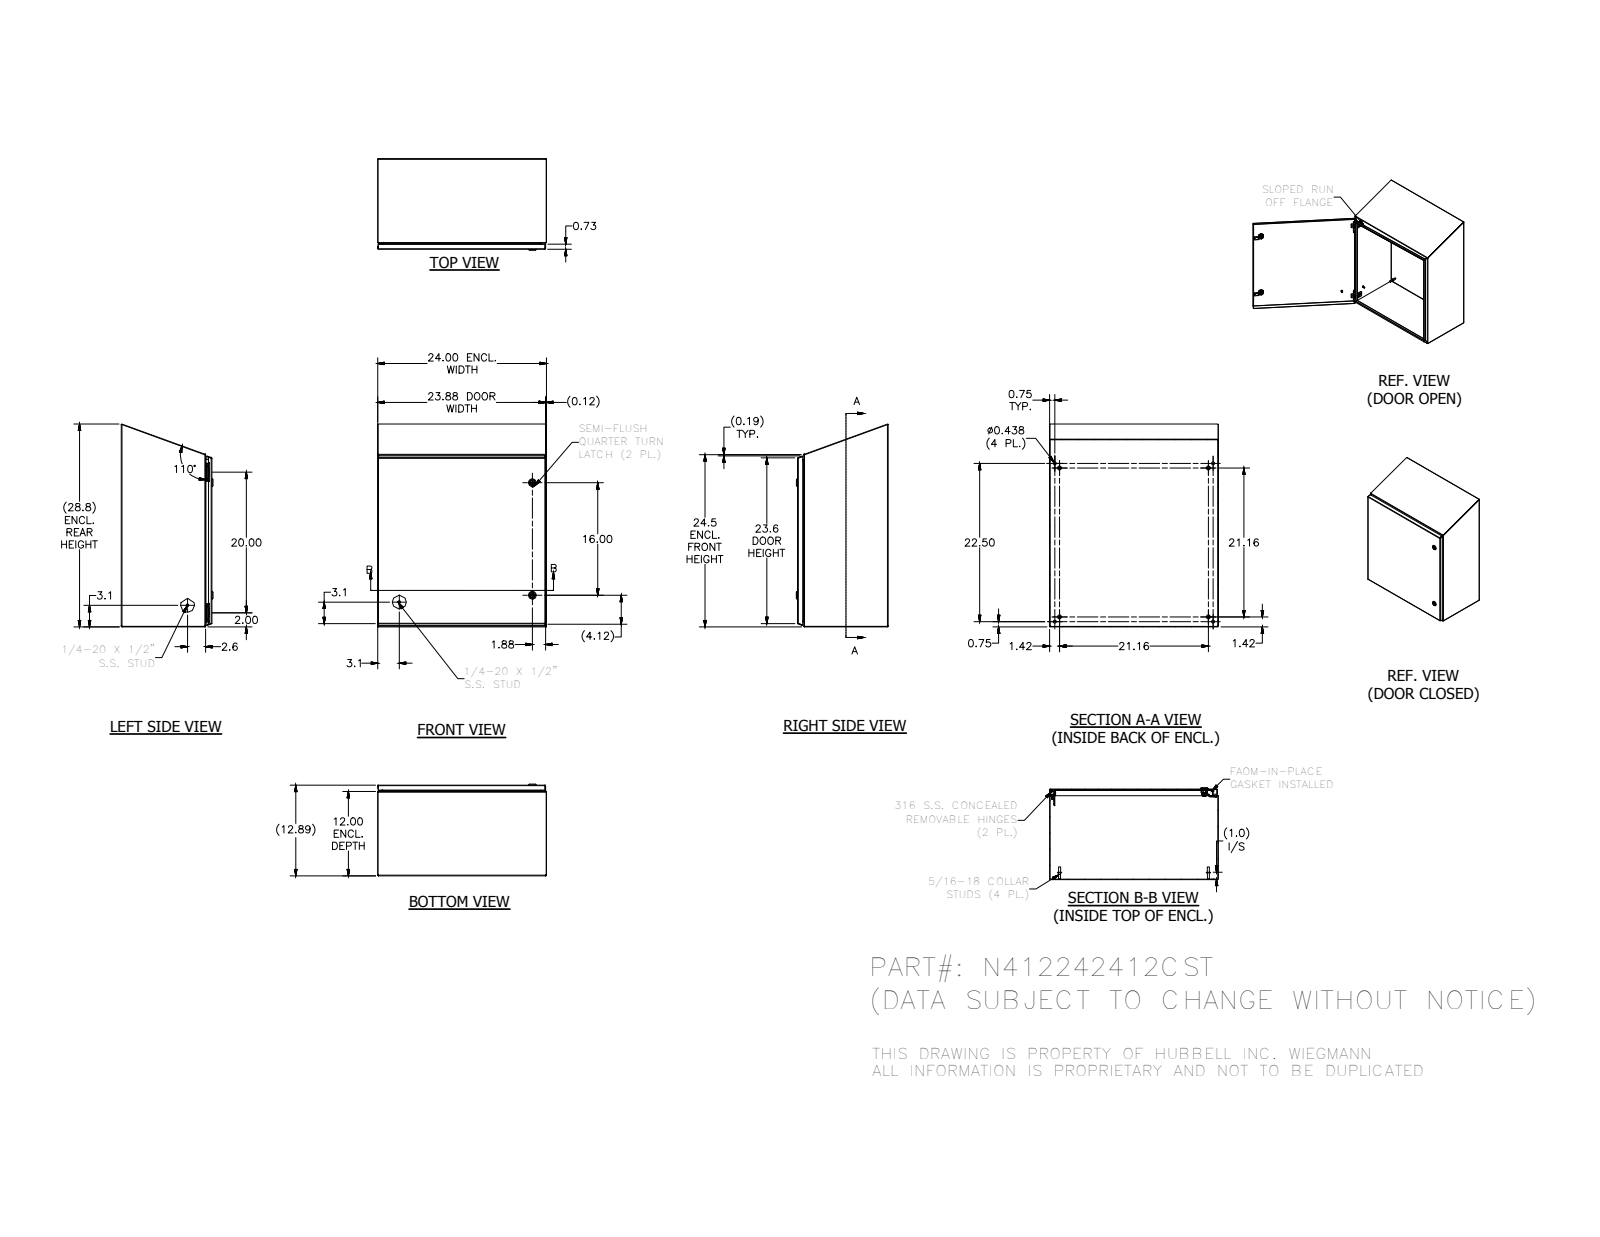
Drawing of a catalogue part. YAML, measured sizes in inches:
part_name: "N412242412CST"
step_written_by: "SolidWorks 2018 (AUTOMOTIVE_DESIGN)"
units: inches
bodies: {solids: 44, faces: 1921, planar: 767, cylindrical: 690, other: 464}
overall_size: [28.847, 24, 13.044]
volume: 201
surface_area: 5451
round_holes:
  - {diameter: 0.093, count: 4}
  - {diameter: 0.152, count: 4}
  - {diameter: 0.167, count: 4}
  - {diameter: 0.172, count: 4}
  - {diameter: 0.187, count: 4}
  - {diameter: 0.437, count: 4}
  - {diameter: 0.156, count: 3}
  - {diameter: 0.197, count: 2}
  - {diameter: 0.315, count: 2}
  - {diameter: 0.394, count: 2}
  - {diameter: 0.402, count: 2}
  - {diameter: 0.634, count: 2}
round_bosses_or_shafts:
  - {diameter: 0.25, count: 10}
  - {diameter: 0.563, count: 4}
  - {diameter: 0.36, count: 4}
  - {diameter: 0.32, count: 4}
  - {diameter: 0.3, count: 4}
  - {diameter: 0.275, count: 4}
  - {diameter: 0.256, count: 4}
  - {diameter: 0.164, count: 4}
partial_cylinders:
  - {radius: 0.012, count: 54}
  - {radius: 0.031, count: 29}
  - {radius: 0.05, count: 26}
  - {radius: 0.02, count: 23}
  - {radius: 0.105, count: 19}
  - {radius: 0.016, count: 18}
  - {radius: 0.125, count: 16}
  - {radius: 0.032, count: 8}
face_to_face_distances: [0.074, 12.813, 23.926, 12.887, 12.739, 23.852, 24, 11.926, 0.887, 0.813]
hole_center_spacings: [20, 22.5, 22.869, 0.5, 0.656, 0.66, 0.984, 1.307]
